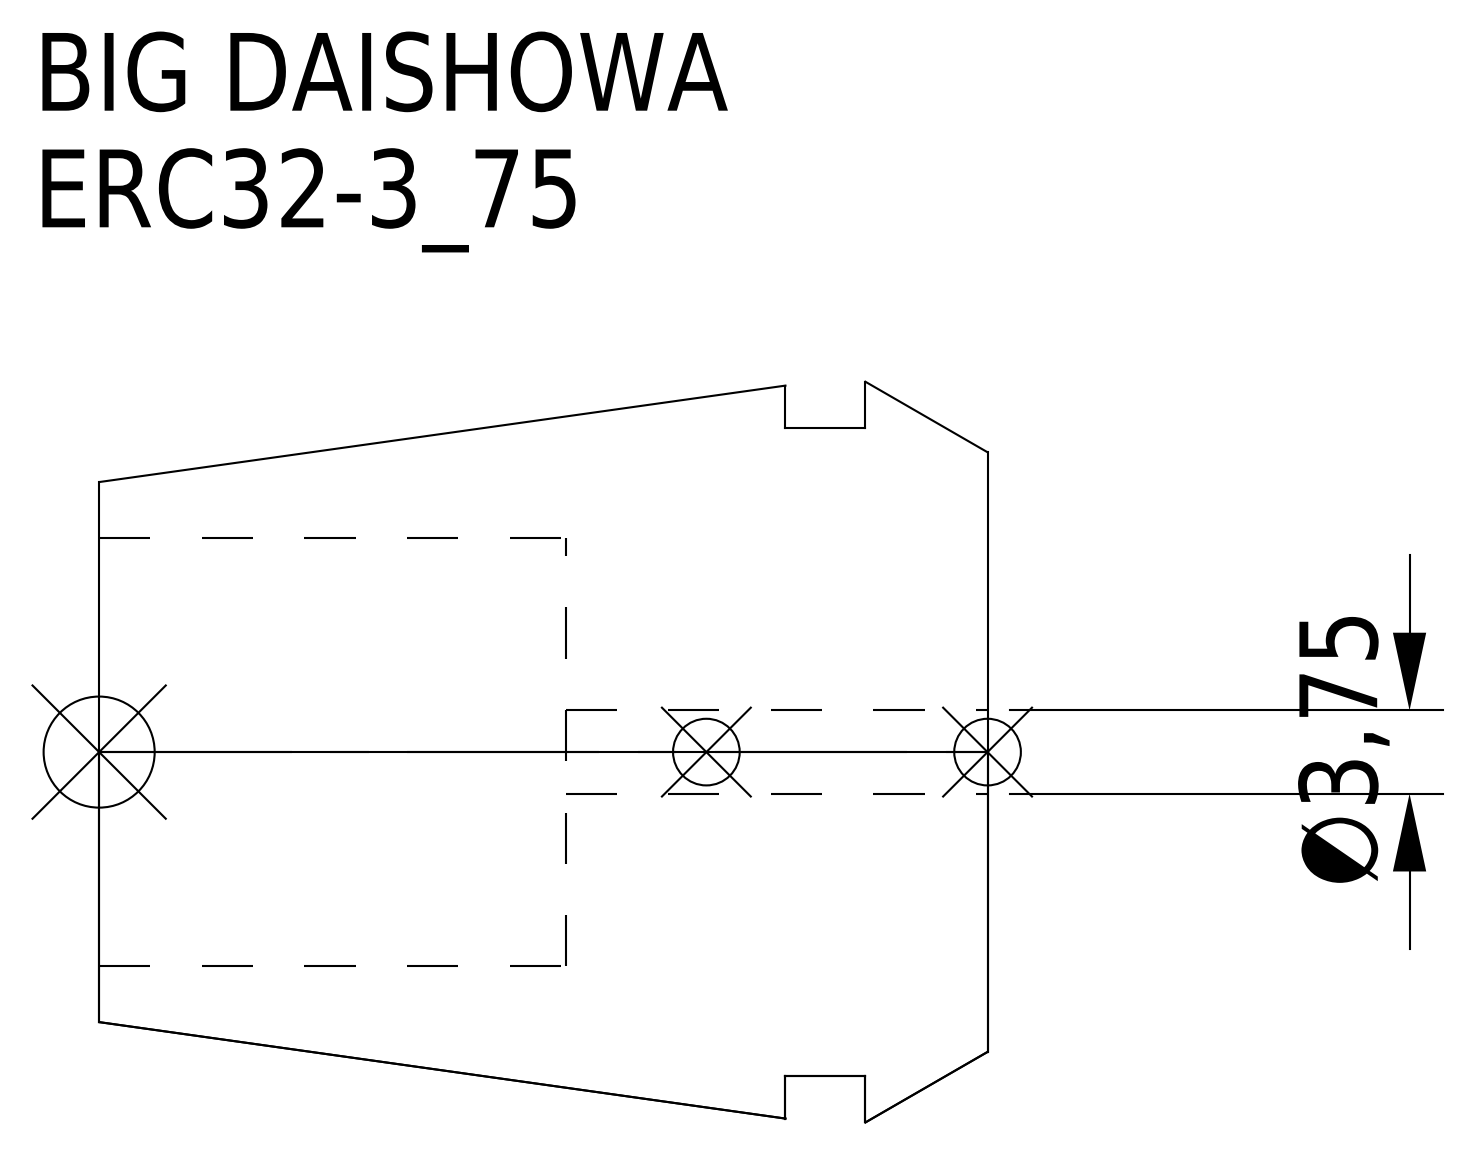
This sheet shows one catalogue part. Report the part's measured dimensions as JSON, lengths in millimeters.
{"part_name": "ERC32-3_75", "step_written_by": "CREO PARAMETRIC BY PTC INC, 2016380 (AUTOMOTIVE_DESIGN)", "units": "millimeters", "bodies": {"solids": 1, "faces": 15, "planar": 5, "cylindrical": 6, "other": 4}, "overall_size": [40, 33.35, 33.35], "volume_mm3": 20089, "surface_area_mm2": 6643, "round_holes": [[3.75, 1], [19.3, 1]], "round_bosses_or_shafts": [[29.2, 1]], "face_to_face_distances": [19, 5.5, 13.5, 9.1, 3.6, 9.9, 40, 34.5, 30.9, 21]}
